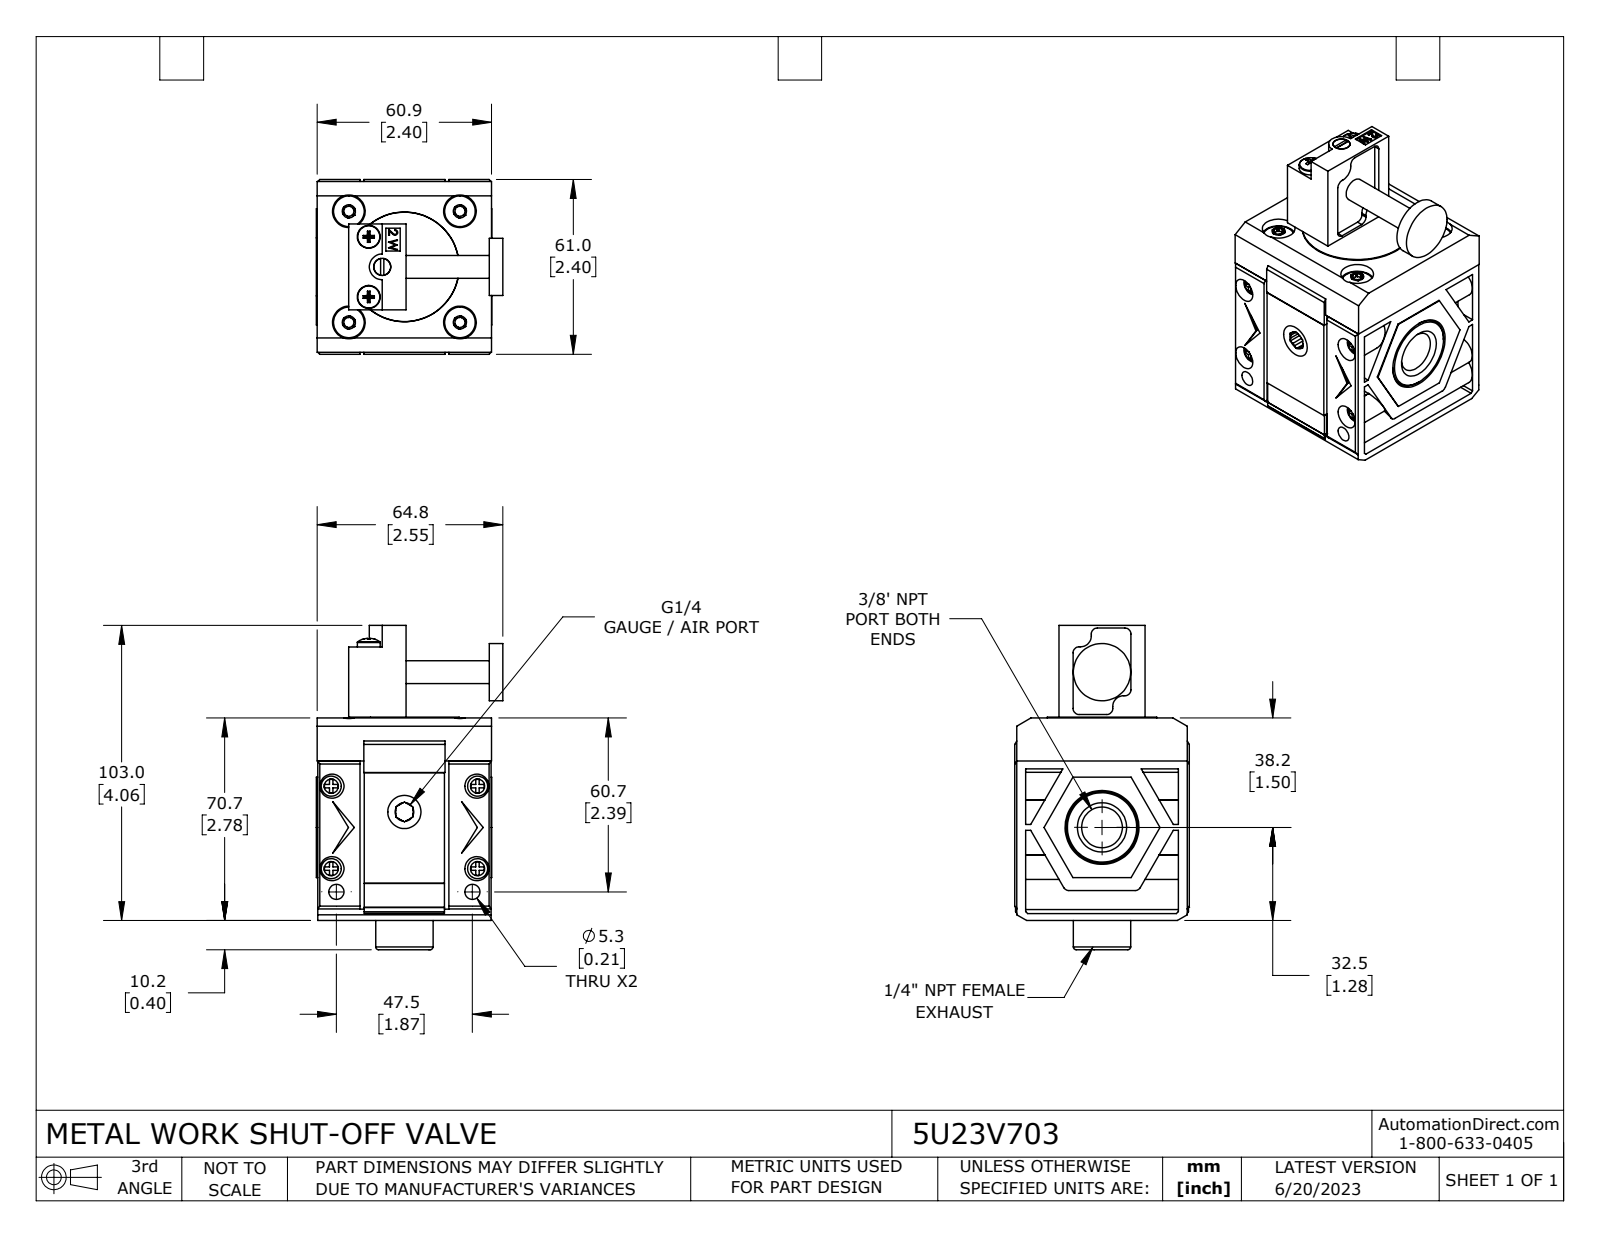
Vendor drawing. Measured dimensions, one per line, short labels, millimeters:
name: 5U23V703
written by: SolidWorks 2021 (CONFIG_CONTROL_DESIGN)
unit: mm
bodies: 13 solids, 858 faces (468 planar, 248 cylindrical, 142 other)
size: 113.2 × 65.1 × 61
volume: 252 200 mm³; area: 72 260 mm²
holes: 4× ⌀3.3, 4× ⌀4.2, 4× ⌀8.4, 4× ⌀11.4, 2× ⌀5.3, 1× ⌀6, 1× ⌀11.5, 1× ⌀11.6, 1× ⌀38.3
bosses: 4× ⌀7, 4× ⌀4.8, 4× ⌀3.8, 3× ⌀8, 2× ⌀20, 1× ⌀38.2, 1× ⌀31.7, 1× ⌀26.3
rounds: 28× R0.3, 6× R2.1, 4× R1.8, 4× R4.9, 2× R2, 2× R3.8, 2× R6.1, 1× R0.7
face distances: 2.4, 61, 60.7, 55.7, 53.3, 0.7, 58.9, 45.7, 15, 10
hole spacings: 27.4, 38.8, 8.3, 22.6, 26.8, 28.8, 32.1, 33.4
